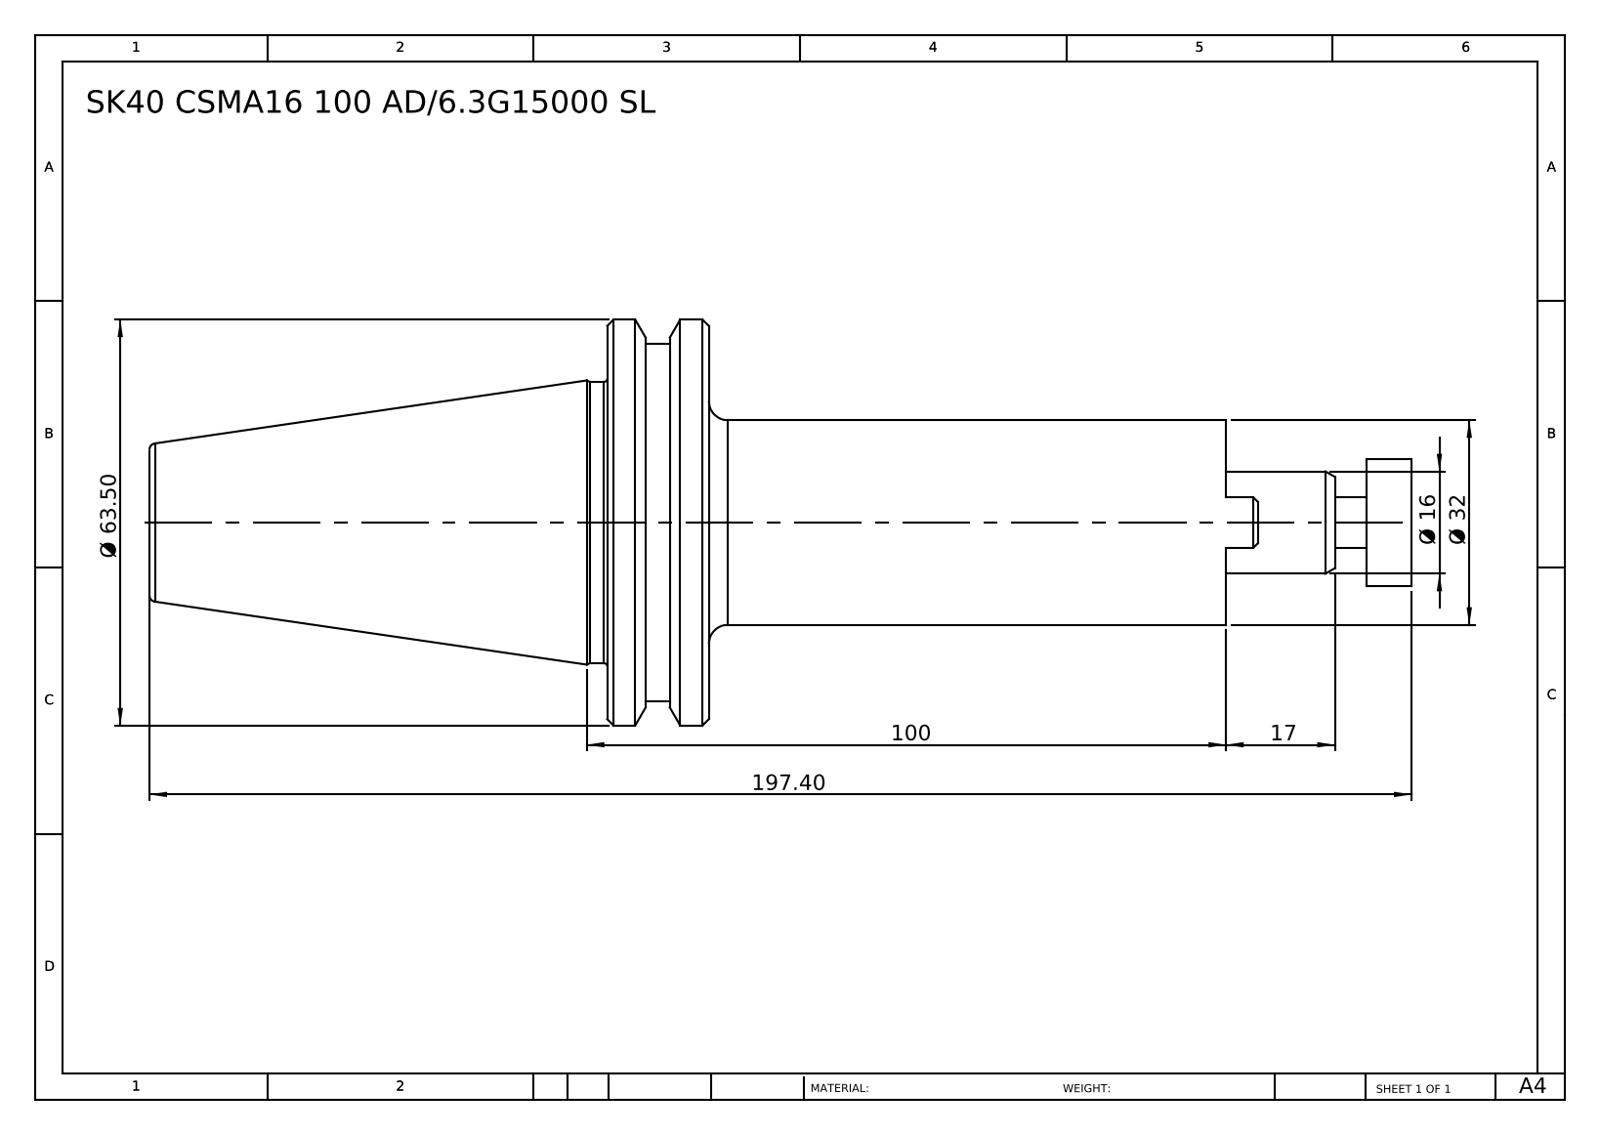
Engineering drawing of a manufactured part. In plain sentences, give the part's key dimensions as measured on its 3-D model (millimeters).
The part is named "SK 40 CSMA16 100 AD-6.3G15000 SL SP". Its 3-D file was written by "SolidWorks 2014 (CONFIG_CONTROL_DESIGN)". It is 1 solid with 58 faces: 20 planar, 16 cylindrical and 22 other. Overall it measures 197.4 by 63.5 by 63.5 millimeters. Its volume is 188 841 cubic millimeters and its surface area 27 006 square millimeters. Round bosses or shafts: 1 of diameter 63.5, 1 of diameter 56, 1 of diameter 44, 1 of diameter 32, 1 of diameter 20, 1 of diameter 16, 1 of diameter 8. The main face-to-face distances are 15.9, 80.9, 96.8, 168.4, 87.5, 71.6, 29, 109.9, 125.8, 197.4.
